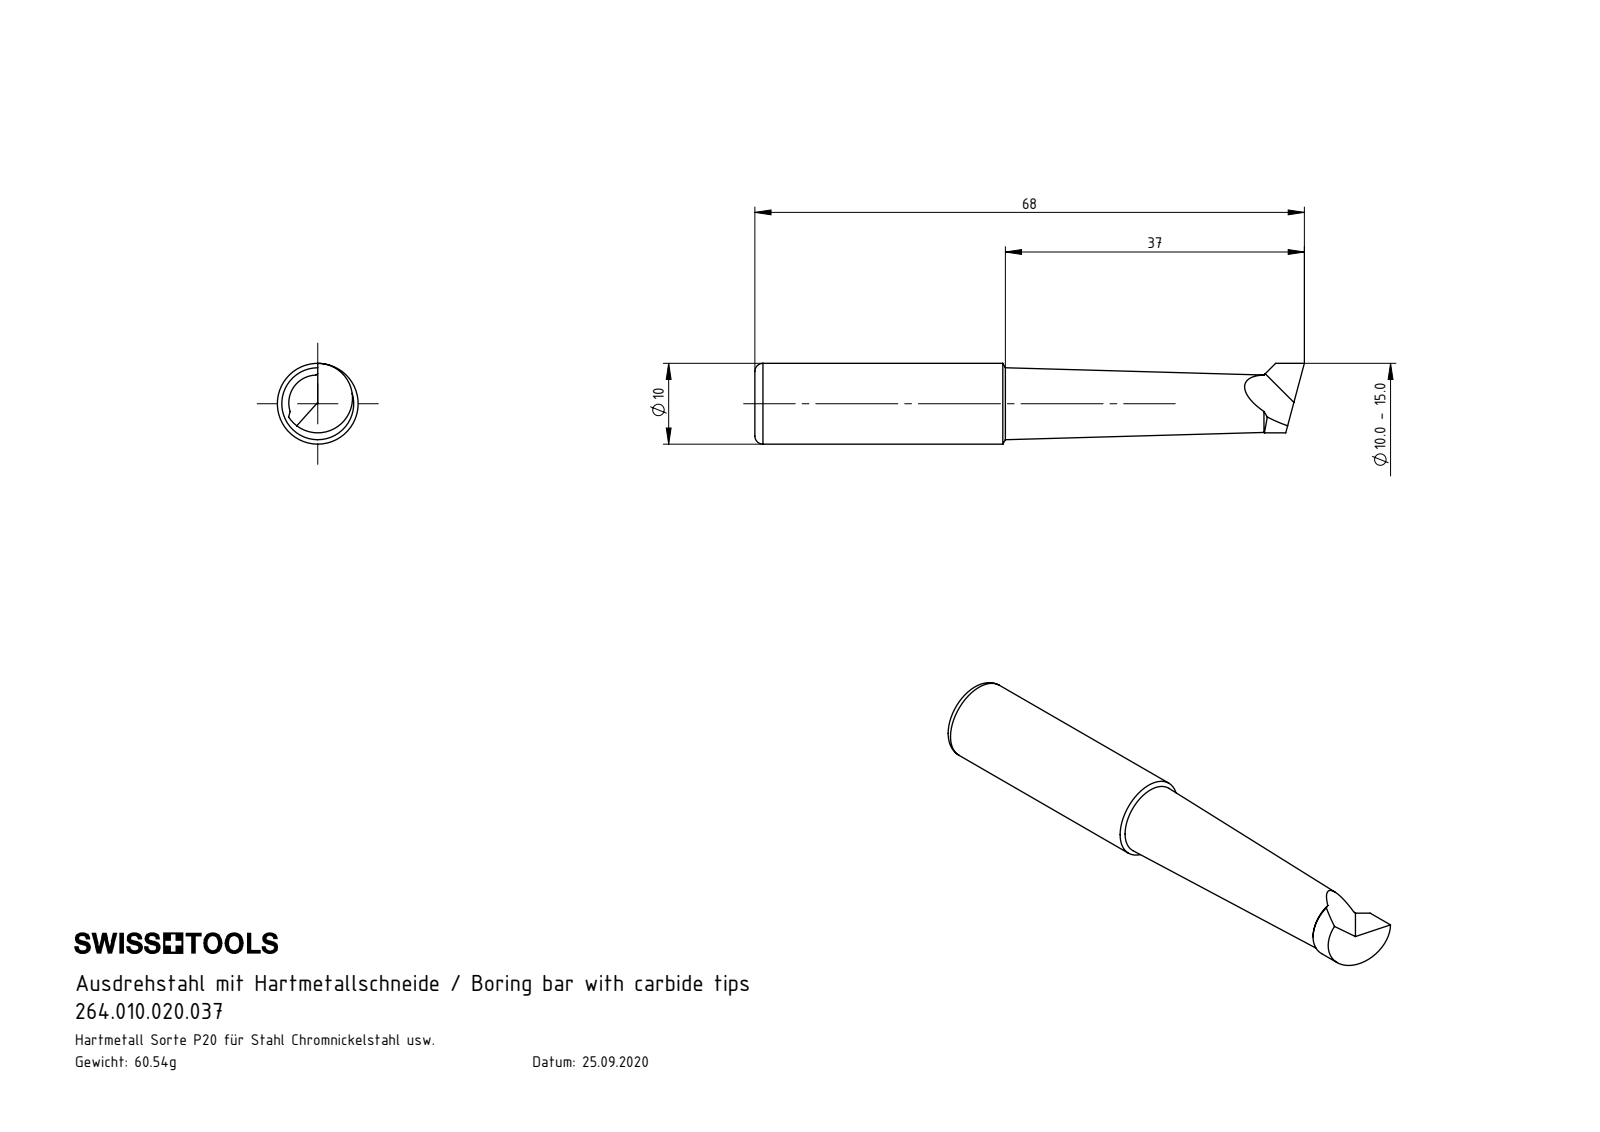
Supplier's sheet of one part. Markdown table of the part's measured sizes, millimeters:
| quantity | value |
| --- | --- |
| part name | U10.B10.002.037 |
| STEP written by | SolidWorks 2017 (AUTOMOTIVE_DESIGN) |
| units | millimeters |
| bodies | 1 solid, 10 faces (4 planar, 2 cylindrical, 4 other) |
| overall size | 68 × 10 × 10 |
| volume | 4 175 mm³ |
| surface area | 1 987 mm² |
| round bosses / shafts (diameter × count) | 10 × 1 |
| partial cylindrical surfaces (radius × count) | 4.3 × 1 |
